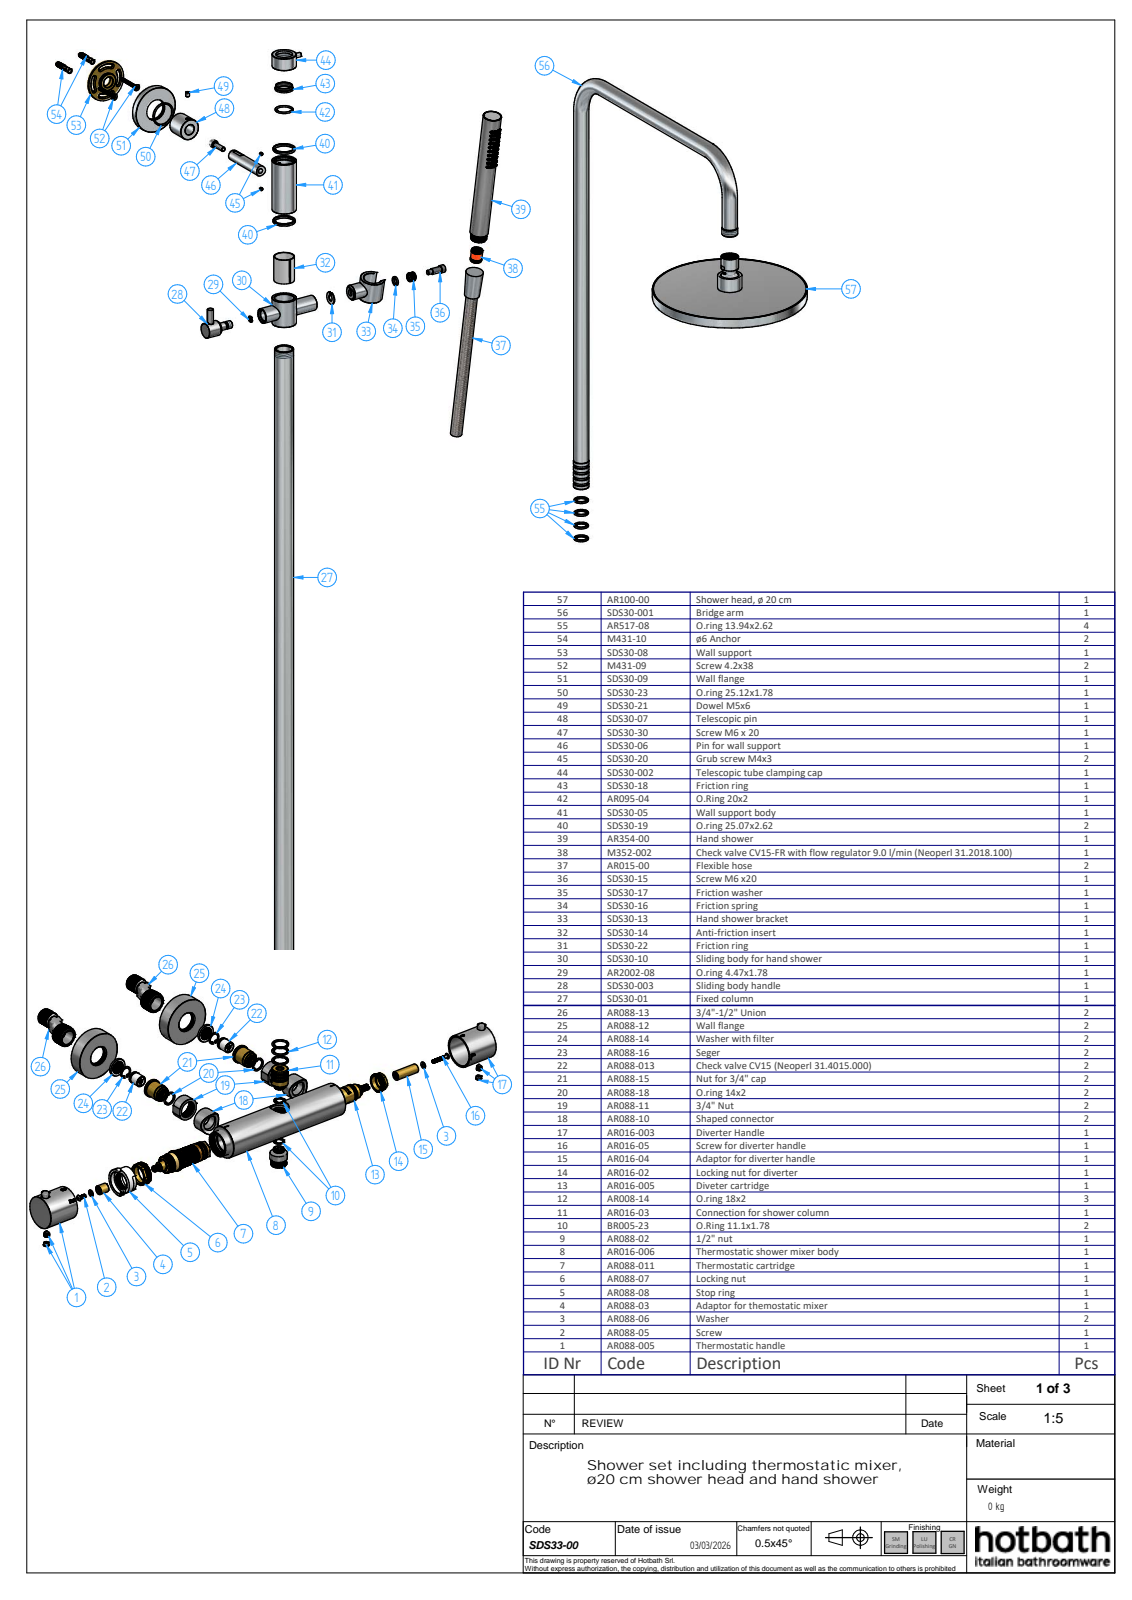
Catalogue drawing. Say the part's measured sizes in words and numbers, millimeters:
The part is named "SDS33-00; AR015-00; AR354-00_oa_0; AR354-001_oa_1 (+8 more)". Its 3-D file was written by "Solid Edge (AUTOMOTIVE_DESIGN)". It is 71 solids with 3347 faces: 949 planar, 854 cylindrical and 1544 other. Overall it measures 1376.79 by 542.75 by 281.39 millimeters. Its volume is 1 049 000 cubic millimeters and its surface area 860 766 square millimeters. Round holes: 126 of diameter 1, 126 of diameter 4.5, 40 of diameter 3.2, 30 of diameter 0.42, 12 of diameter 0.62, 7 of diameter 6, 7 of diameter 8, 6 of diameter 3.3, 5 of diameter 2.5, 5 of diameter 3.24, 4 of diameter 4.8, 4 of diameter 13. Round bosses or shafts: 7 of diameter 4, 5 of diameter 6, 4 of diameter 7, 3 of diameter 20, 2 of diameter 64, 2 of diameter 32, 2 of diameter 30, 2 of diameter 24. Partial cylindrical surfaces (rounded edges, fillets, slot ends): 6 of radius 0.2, 5 of radius 11, 4 of radius 0.35, 3 of radius 0.59, 2 of radius 0.15, 2 of radius 0.22, 2 of radius 0.23, 2 of radius 0.28. The main face-to-face distances are 5, 1, 12.5, 11.5, 4, 6.4, 6.1, 5.1, 3, 8.5. The hole center spacings are 7.21, 12, 1.01, 0.7, 6, 1.58, 2.29, 4.
